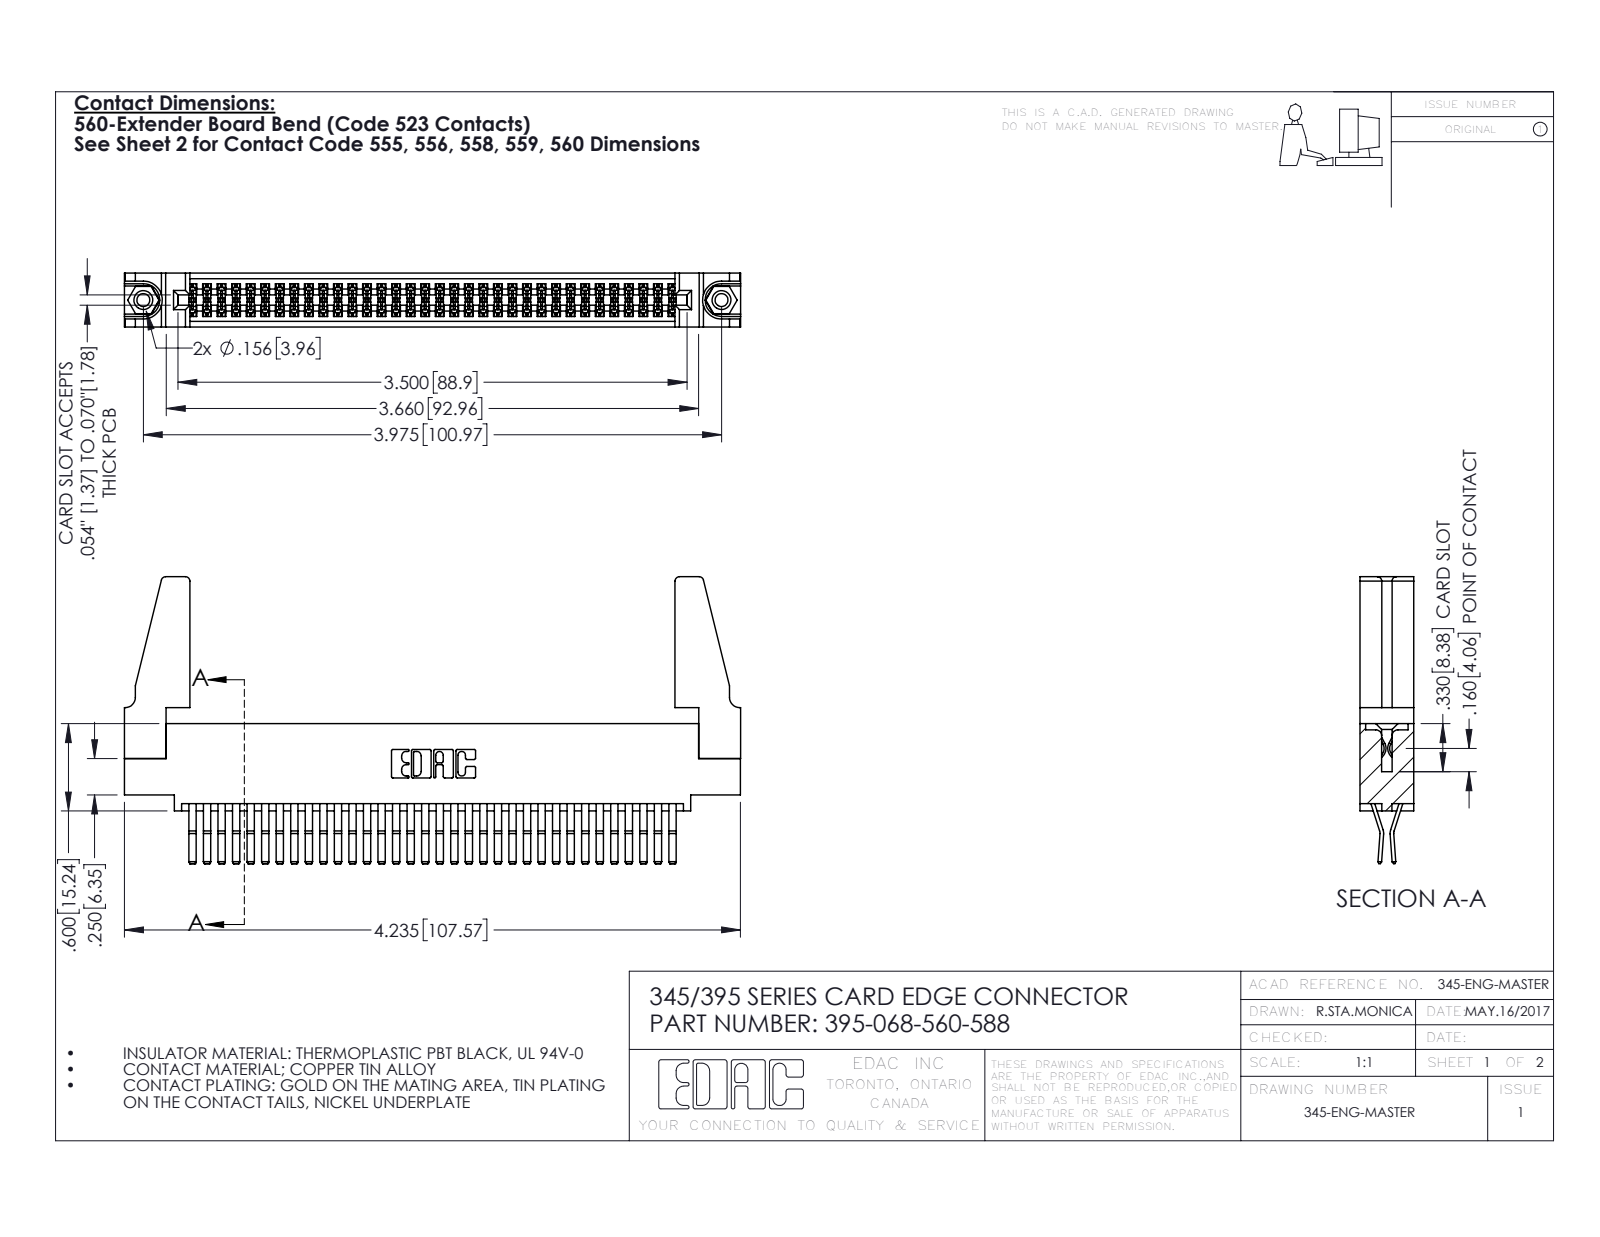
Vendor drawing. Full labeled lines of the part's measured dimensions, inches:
Part name (STEP PRODUCT): 345-292-001_560 Tail; 345-220-078_345-220-088; 395-068-560-588; 345-250-001_345-250-001-102 (+1 more)
STEP written by: SolidWorks 2016 (CONFIG_CONTROL_DESIGN)
Units: inches
Bodies: 73 solids, 3790 faces (2400 planar, 1374 cylindrical, 16 other)
Overall size (bounding box): 4.236 × 1.972 × 0.37
Volume: 0.854 in³ · Surface area: 31.15 in²
Round holes (diameter × count): ⌀0.089 ×2, ⌀0.125 ×2, ⌀0.156 ×2, ⌀0.064 ×1
Round bosses / shafts (diameter × count): ⌀0.155 ×2
Partial cylindrical surfaces — rounded edges, fillets, slot ends (radius × count): R0.006 ×102, R0.01 ×22, R0.03 ×8, R0.007 ×6, R0.031 ×6, R0.026 ×3, R0.01 ×2, R0.014 ×2
Main face-to-face distances: 0.072, 0.298, 0.025, 0.37, 0.2, 0.098, 0.272, 0.225, 0.175, 0.149
Hole centre spacings: 0.27, 3.74, 3.975
